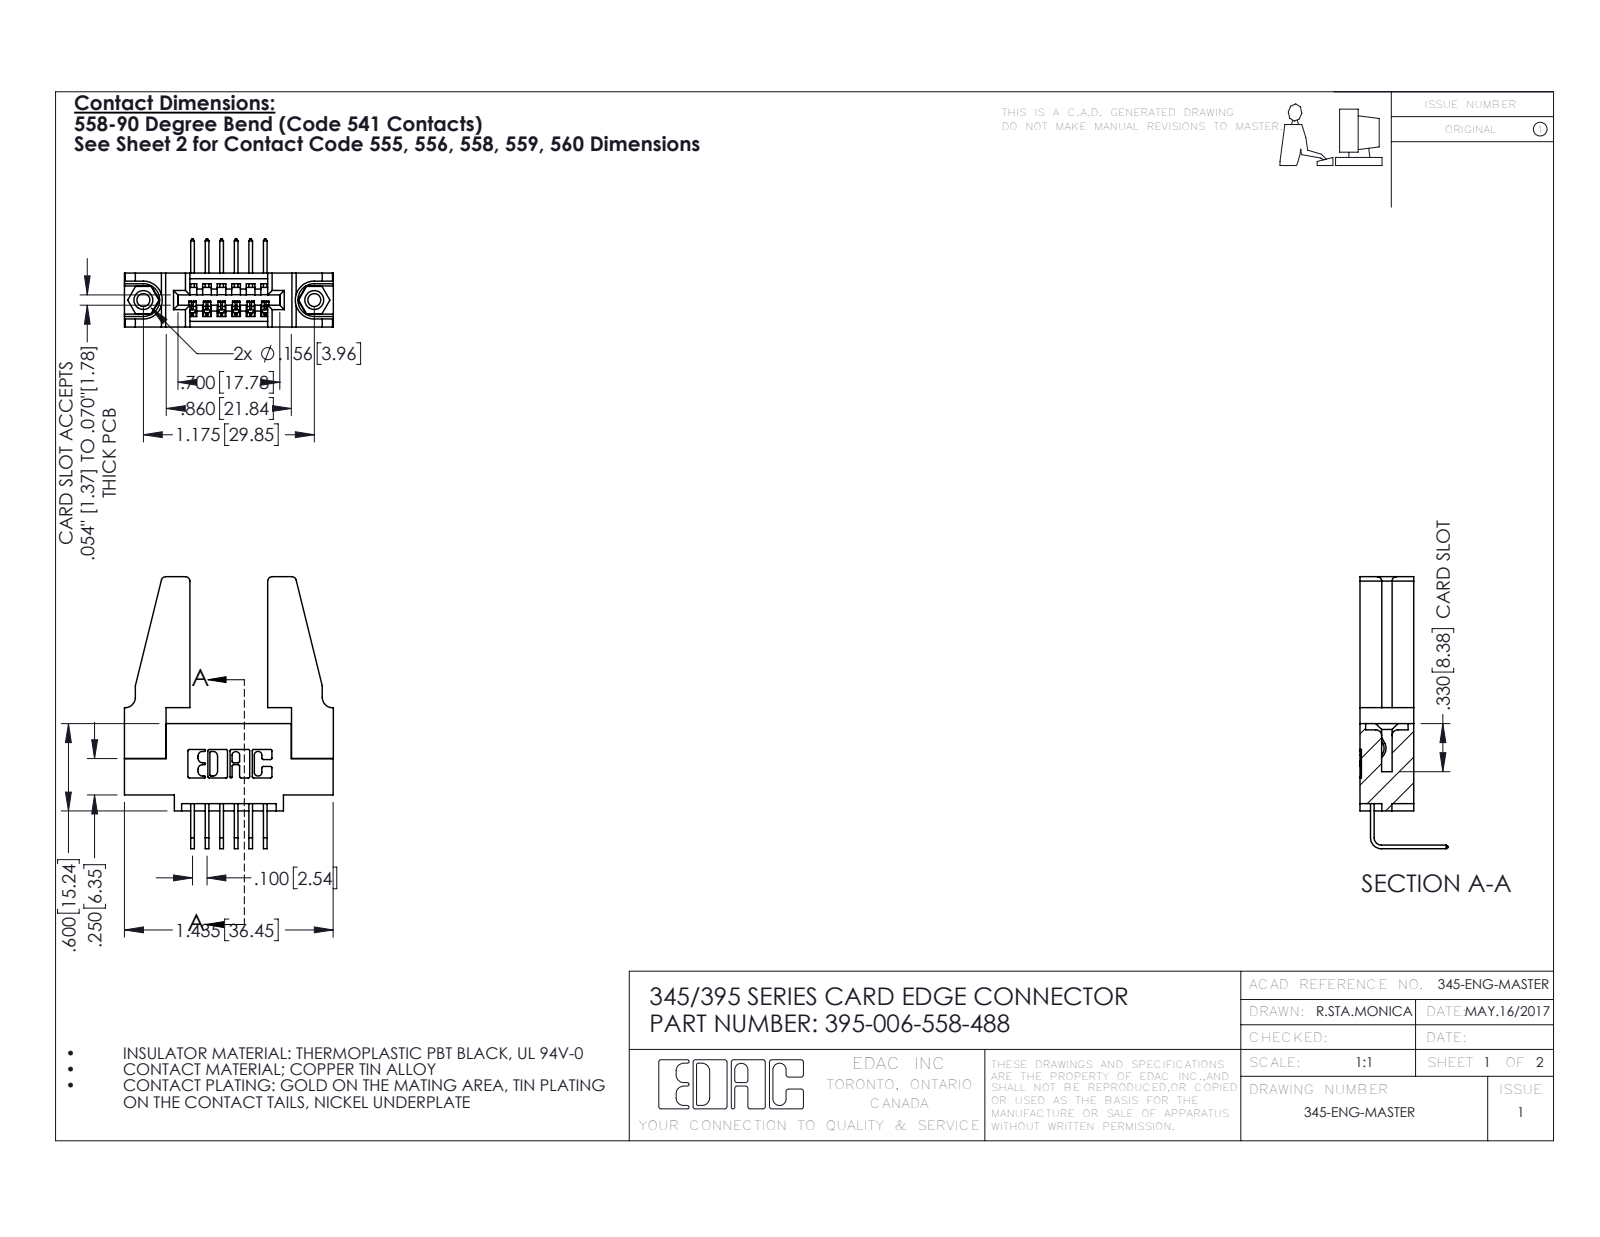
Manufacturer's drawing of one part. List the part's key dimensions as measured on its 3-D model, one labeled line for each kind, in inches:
Part name (STEP PRODUCT): 345-220-078_345-220-088; 345-250-001_345-250-001-102; 345 Part_0.110 Offset - 0.156 Dia-TH; 345-292-001_558 Tail - 2 (+1 more)
STEP written by: SolidWorks 2016 (CONFIG_CONTROL_DESIGN)
Units: inches
Bodies: 11 solids, 614 faces (408 planar, 190 cylindrical, 16 other)
Overall size (bounding box): 1.869 × 1.436 × 0.605
Volume: 0.389 in³ · Surface area: 10.82 in²
Round holes (diameter × count): ⌀0.089 ×2, ⌀0.125 ×2, ⌀0.156 ×2, ⌀0.064 ×1
Round bosses / shafts (diameter × count): ⌀0.155 ×2
Partial cylindrical surfaces — rounded edges, fillets, slot ends (radius × count): R0.01 ×22, R0.006 ×12, R0.03 ×8, R0.007 ×6, R0.031 ×6, R0.026 ×3, R0.031 ×2, R0.04 ×2
Main face-to-face distances: 0.37, 0.072, 0.298, 0.2, 0.15, 0.148, 0.098, 0.272, 0.025, 0.22
Hole centre spacings: 0.27, 0.946, 1.175
